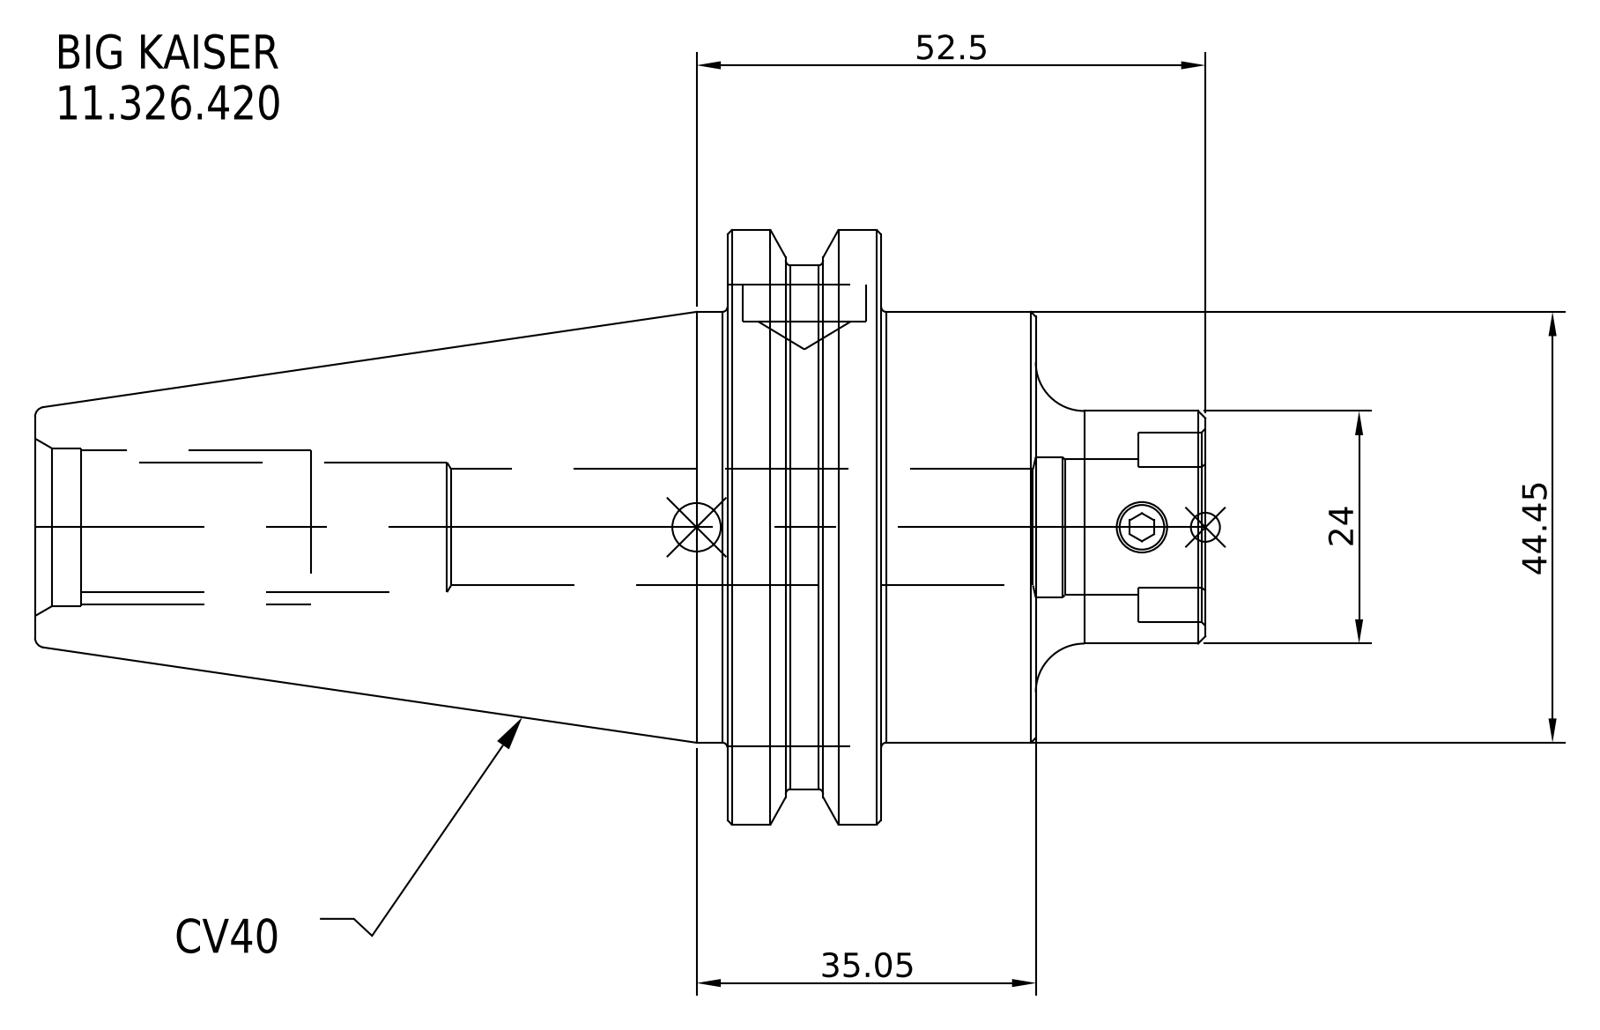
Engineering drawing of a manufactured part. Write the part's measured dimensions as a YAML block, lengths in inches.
part_name: "11_326_420"
step_written_by: "SolidWorks 2021 (CONFIG_CONTROL_DESIGN)"
units: inches
bodies: {solids: 1, faces: 27, planar: 7, cylindrical: 12, other: 8}
overall_size: [4.754, 2.5, 2.5]
volume: 9.183
surface_area: 31.81
round_bosses_or_shafts:
  - {diameter: 2.5, count: 1}
  - {diameter: 2.219, count: 1}
  - {diameter: 1.75, count: 1}
  - {diameter: 0.945, count: 1}
face_to_face_distances: [0.625, 0.63, 1.255, 4.067, 3.437, 2.812, 0.687, 1.317, 1.942, 4.754]
